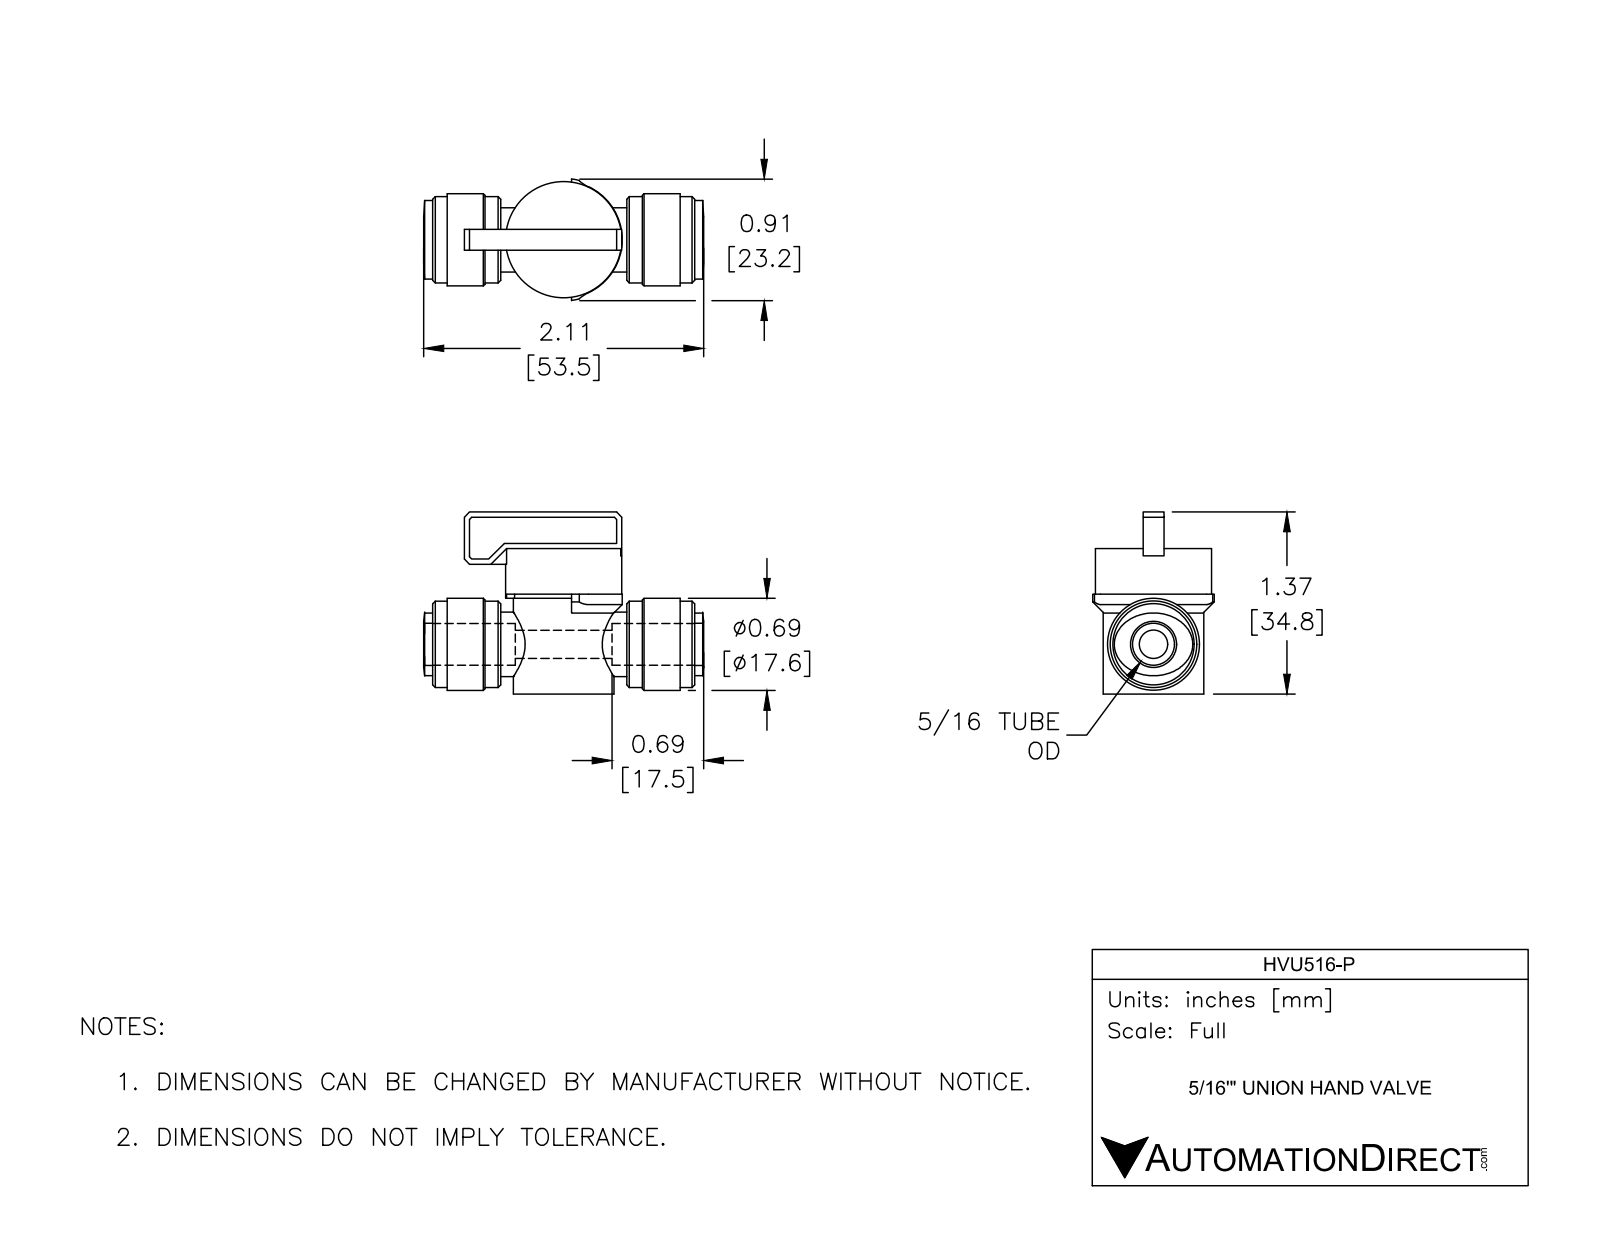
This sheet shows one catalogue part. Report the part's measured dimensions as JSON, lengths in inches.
{"part_name": "HVU516-P", "step_written_by": "SolidWorks 2017 (AUTOMOTIVE_DESIGN)", "units": "inches", "bodies": {"solids": 1, "faces": 126, "planar": 64, "cylindrical": 32, "other": 30}, "overall_size": [2.106, 1.37, 0.914], "volume_in3": 0.889, "surface_area_in2": 10.29, "round_holes": [[0.213, 1], [0.315, 1]], "round_bosses_or_shafts": [[0.874, 1], [0.756, 1], [0.693, 1], [0.65, 1], [0.484, 1]], "partial_cylinders_radius": [[0.276, 2], [0.441, 1], [0.461, 1]], "face_to_face_distances": [1.094, 0.071, 0.039, 0.512, 0.043, 0.114, 1.35, 0.11, 0.276, 1.37]}
